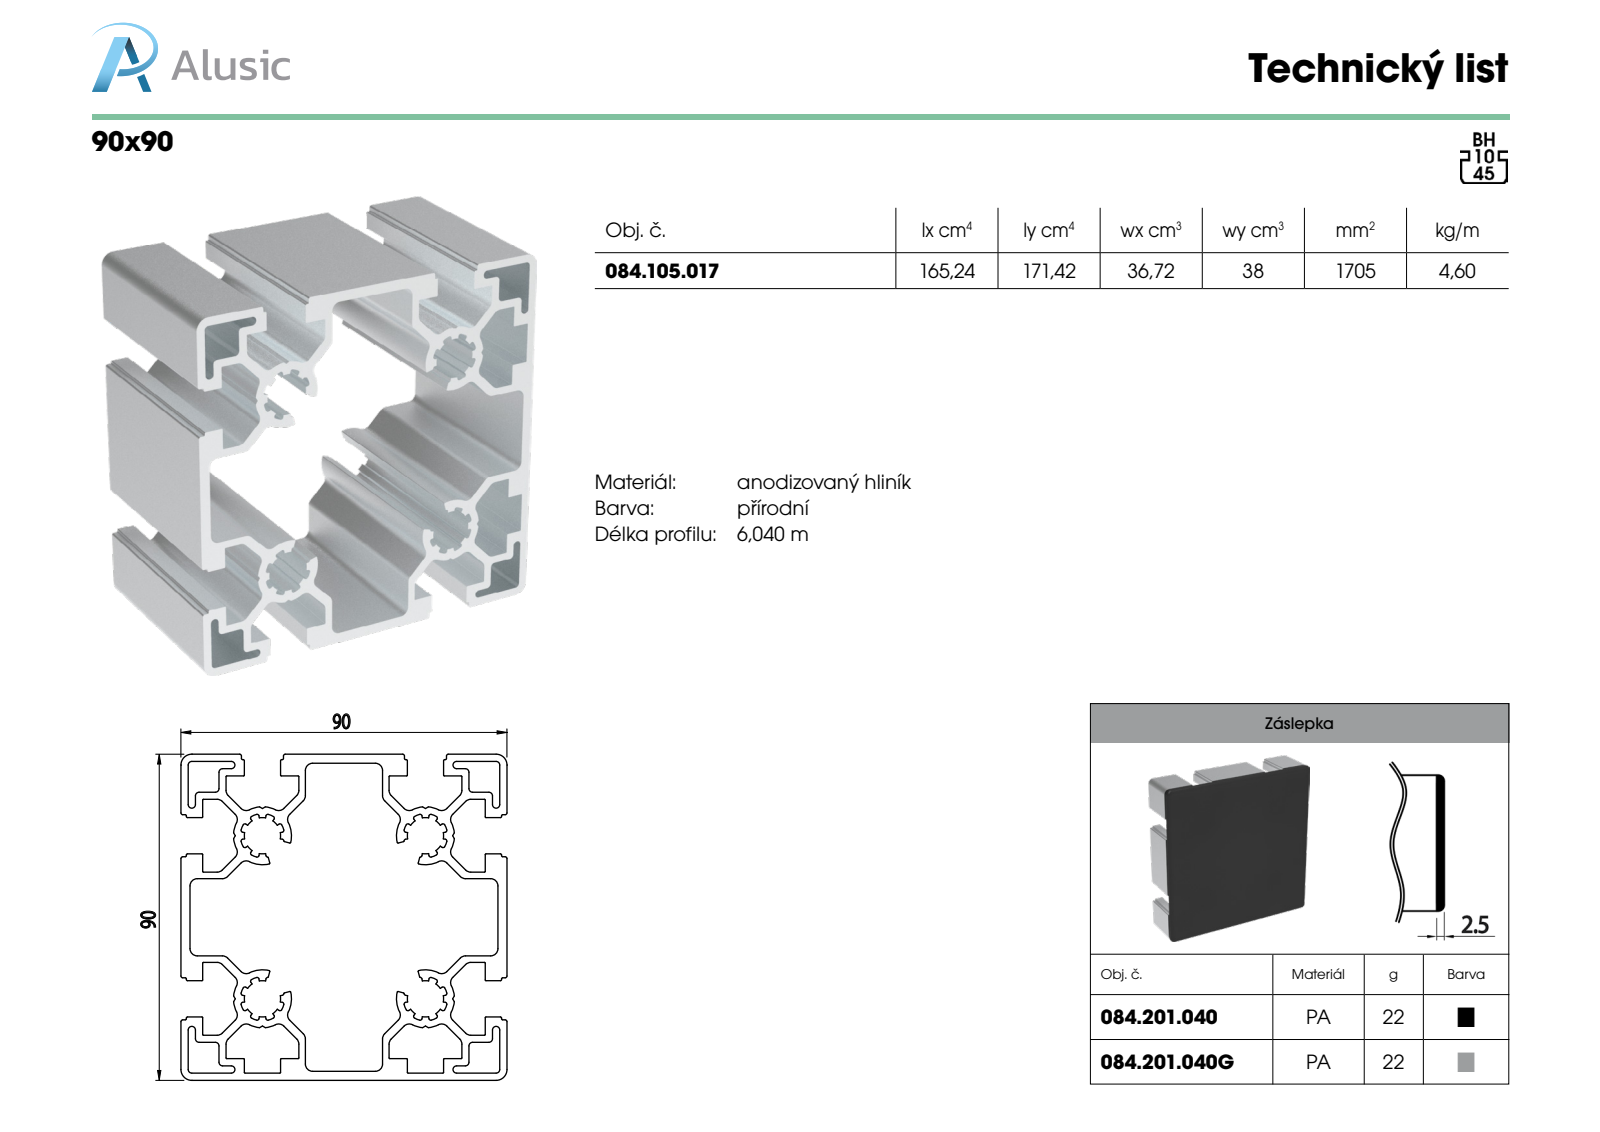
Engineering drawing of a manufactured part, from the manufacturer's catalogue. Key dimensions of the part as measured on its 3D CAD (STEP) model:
Part name (STEP PRODUCT): 084.105.017
STEP written by: SolidWorks 2018 (AUTOMOTIVE_DESIGN)
Units: millimetres
Bodies: 1 solid, 558 faces (226 planar, 332 cylindrical, 0 other)
Overall size (bounding box): 100 × 90 × 90
Volume: 170 490 mm³ · Surface area: 142 352 mm²
Partial cylindrical surfaces — rounded edges, fillets, slot ends (radius × count): R0.5 ×68, R2 ×56, R0.2 ×52, R0.3 ×24, R1 ×24, R3 ×4, R5 ×4, R6.1 ×4
Main face-to-face distances: 90, 2, 88, 6, 84, 4, 82, 2.5, 87.5, 0.5
